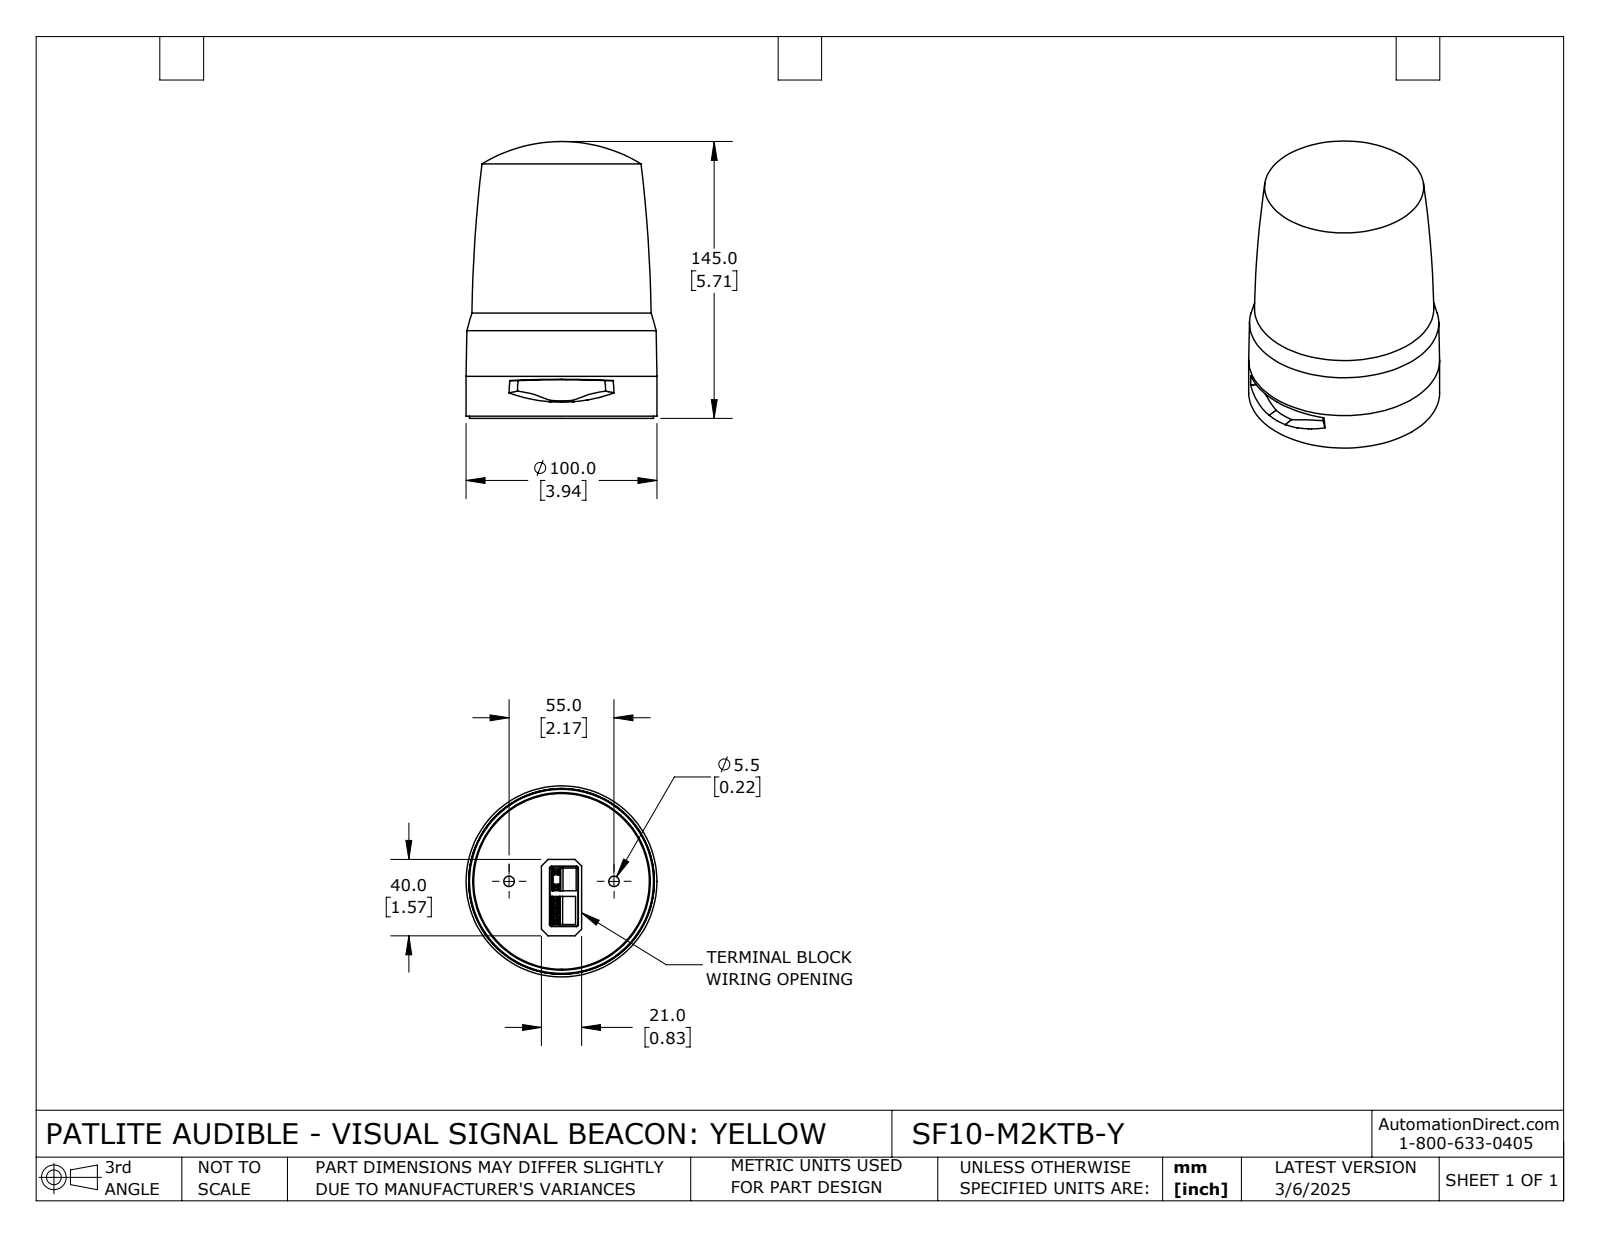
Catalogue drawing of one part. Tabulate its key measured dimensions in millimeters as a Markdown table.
| quantity | value |
| --- | --- |
| part name | SF10-M2KTB-Y |
| STEP written by | SolidWorks 2024 (CONFIG_CONTROL_DESIGN) |
| units | millimeters |
| bodies | 2 solids, 275 faces (174 planar, 31 cylindrical, 70 other) |
| overall size | 145 × 100 × 100 |
| volume | 875 277 mm³ |
| surface area | 79 857 mm² |
| round holes (diameter × count) | 5.5 × 2, 13 × 2, 93 × 1 |
| round bosses / shafts (diameter × count) | 100 × 1, 96.4 × 1, 94.5 × 1, 93.2 × 1, 92 × 1 |
| partial cylindrical surfaces (radius × count) | 1 × 4, 0.3 × 2, 44.75 × 1, 45 × 1 |
| main face-to-face distances | 6.3, 18.2, 11.9, 5.6, 12.6, 5.1, 0.4, 4.7, 1.2, 17 |
| hole center spacings | 27.5, 55 |
